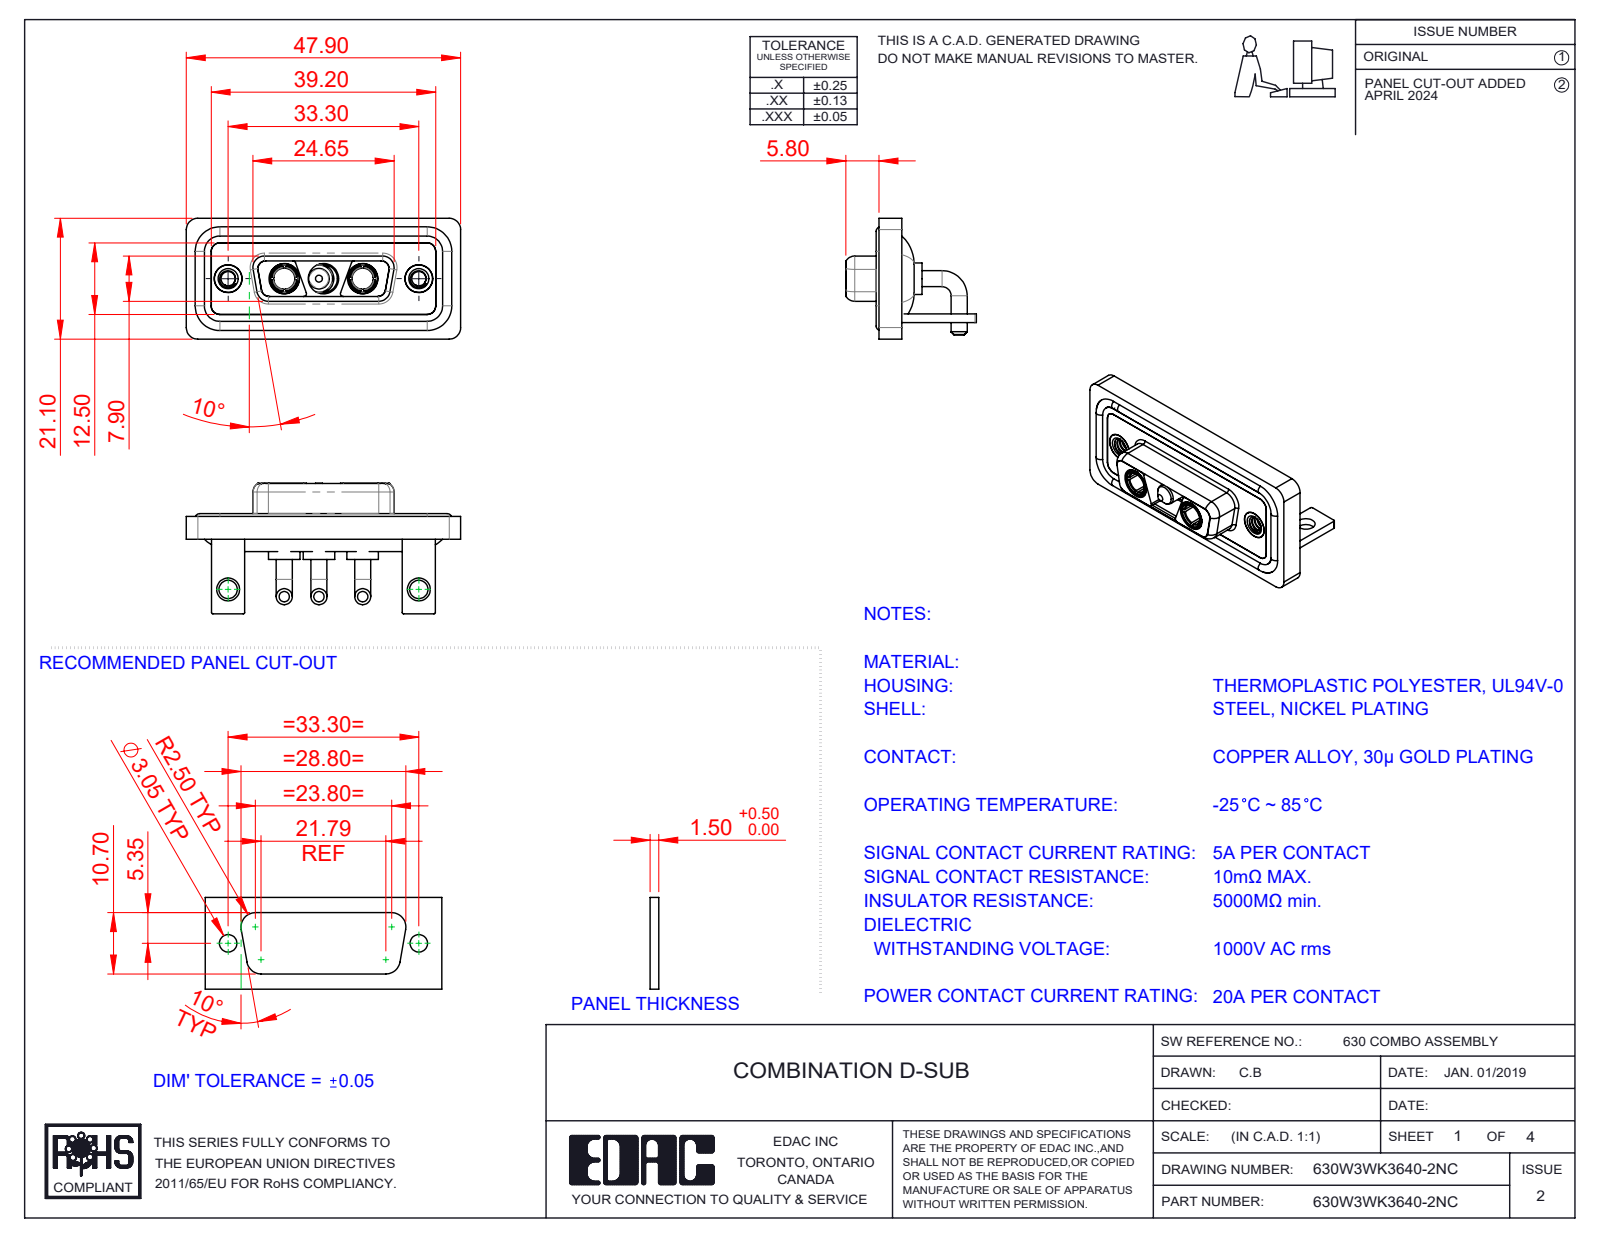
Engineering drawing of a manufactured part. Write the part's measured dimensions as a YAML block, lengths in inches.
part_name: "Power Socket_20A RA; 630Combo Shell Rear_15 Contacts; 630Combo Stabilizer Bracket_50 Contacts; 630Combo Housing_3WK3 (+5 more)"
step_written_by: "SolidWorks 2023 (CONFIG_CONTROL_DESIGN)"
units: inches
bodies: {solids: 15, faces: 637, planar: 198, cylindrical: 286, other: 153}
overall_size: [1.886, 0.898, 0.831]
volume: 0.39
surface_area: 16.24
round_holes:
  - {diameter: 0.191, count: 5}
  - {diameter: 0.209, count: 3}
  - {diameter: 0.098, count: 2}
  - {diameter: 0.126, count: 2}
  - {diameter: 0.146, count: 2}
  - {diameter: 0.157, count: 2}
  - {diameter: 0.159, count: 2}
  - {diameter: 0.197, count: 2}
round_bosses_or_shafts:
  - {diameter: 0.11, count: 6}
  - {diameter: 0.063, count: 4}
  - {diameter: 0.217, count: 3}
  - {diameter: 0.205, count: 3}
  - {diameter: 0.187, count: 3}
  - {diameter: 0.148, count: 3}
  - {diameter: 0.195, count: 2}
  - {diameter: 0.195, count: 2}
partial_cylinders:
  - {radius: 0.079, count: 21}
  - {radius: 0.059, count: 18}
  - {radius: 0.01, count: 16}
  - {radius: 0.053, count: 12}
  - {radius: 0.02, count: 9}
  - {radius: 0.063, count: 8}
  - {radius: 0.024, count: 4}
  - {radius: 0.026, count: 4}
face_to_face_distances: [0.016, 0.114, 0.059, 0.146, 0.071, 0.043, 0.161, 0.063, 0.098, 0.055]
hole_center_spacings: [0.27, 0.386, 0.656, 0.925, 1.311, 0.539]
